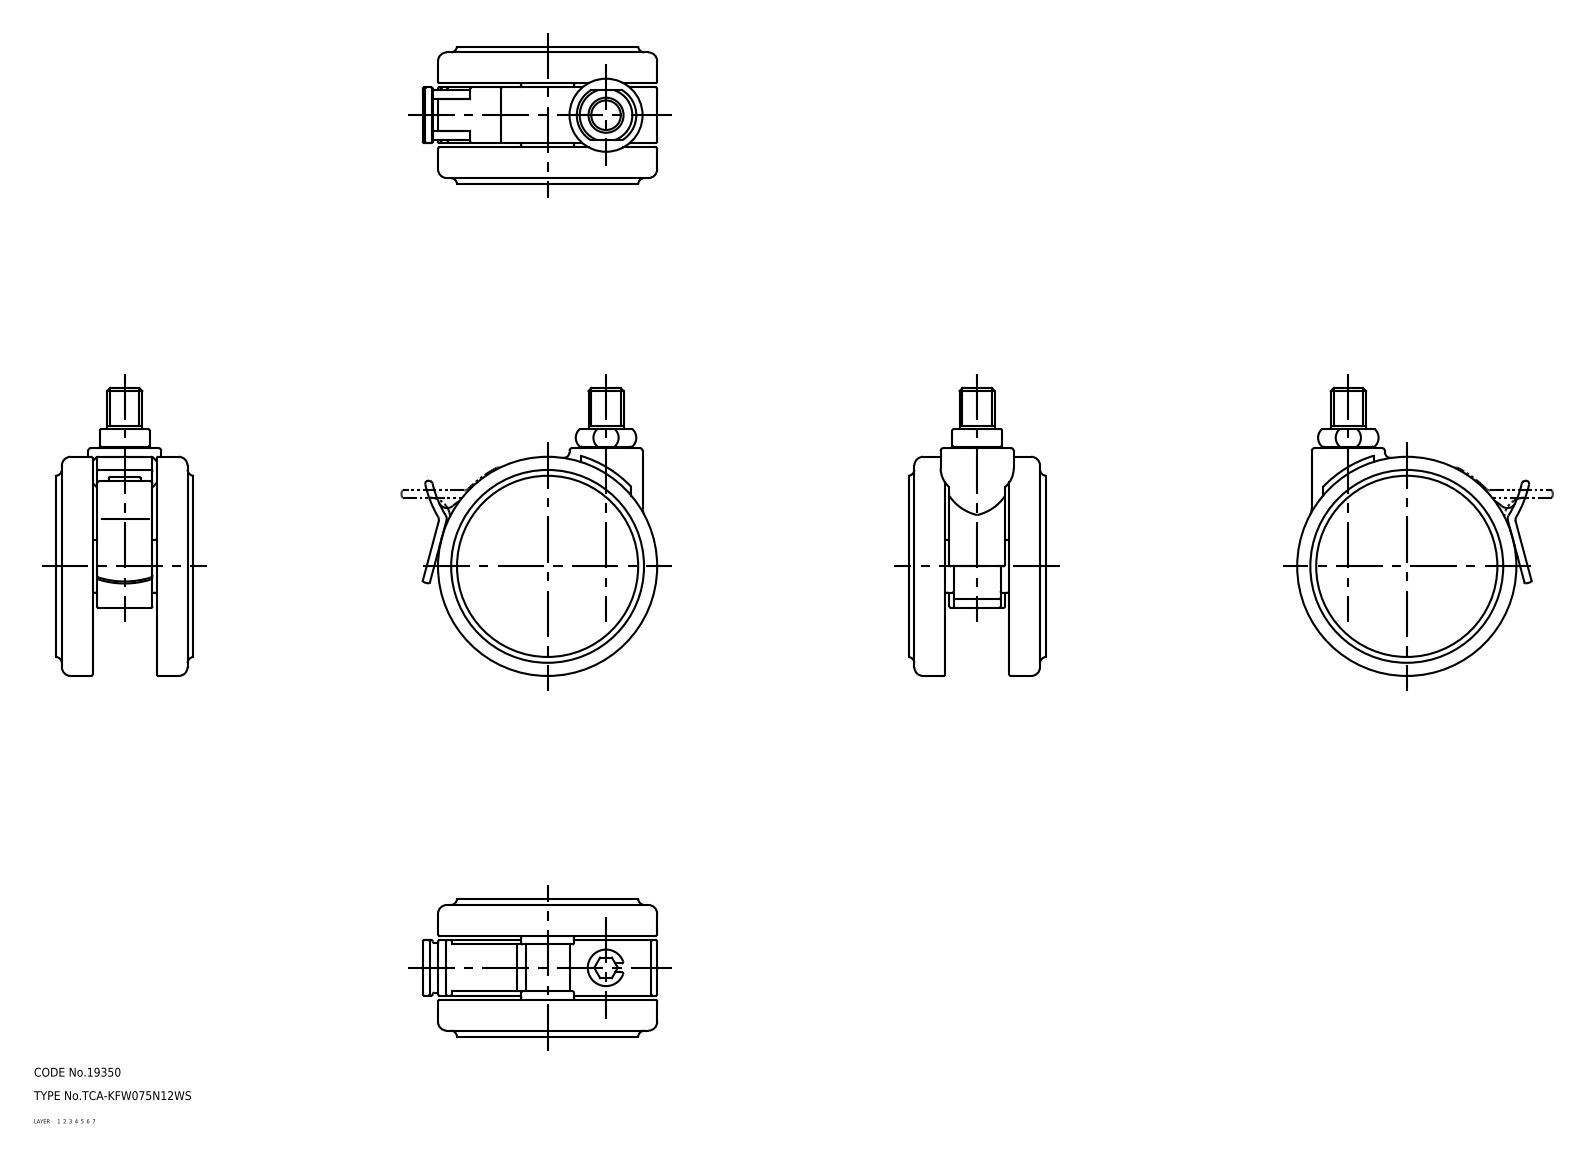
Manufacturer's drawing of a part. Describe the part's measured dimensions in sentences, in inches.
The part is named "TCA_KFW075N12WS; lever; wheel_mr; wheel (+1 more)". Its 3-D file was written by "SolidWorks 2015 (AUTOMOTIVE_DESIGN)". It is 5 solids with 269 faces: 62 planar, 107 cylindrical and 100 other. Overall it measures 3.878 by 3.159 by 1.85 inches. Its volume is 9.515 cubic inches and its surface area 61.38 square inches. Round holes: 1 of diameter 0.236, 1 of diameter 1.693. Round bosses or shafts: 1 of diameter 2.953, 1 of diameter 0.984, 1 of diameter 0.709, 1 of diameter 0.669, 1 of diameter 0.492, 1 of diameter 0.472. Partial cylindrical surfaces (rounded edges, fillets, slot ends): 43 of radius 0.02, 2 of radius 0.039, 2 of radius 0.079, 2 of radius 0.118, 2 of radius 1.398, 1 of radius 0.114, 1 of radius 0.276, 1 of radius 0.297. The main face-to-face distances are 0.492, 1.358, 0.059, 0.866, 0.118, 0.551, 0.748, 0.807, 1.85, 1.299.
